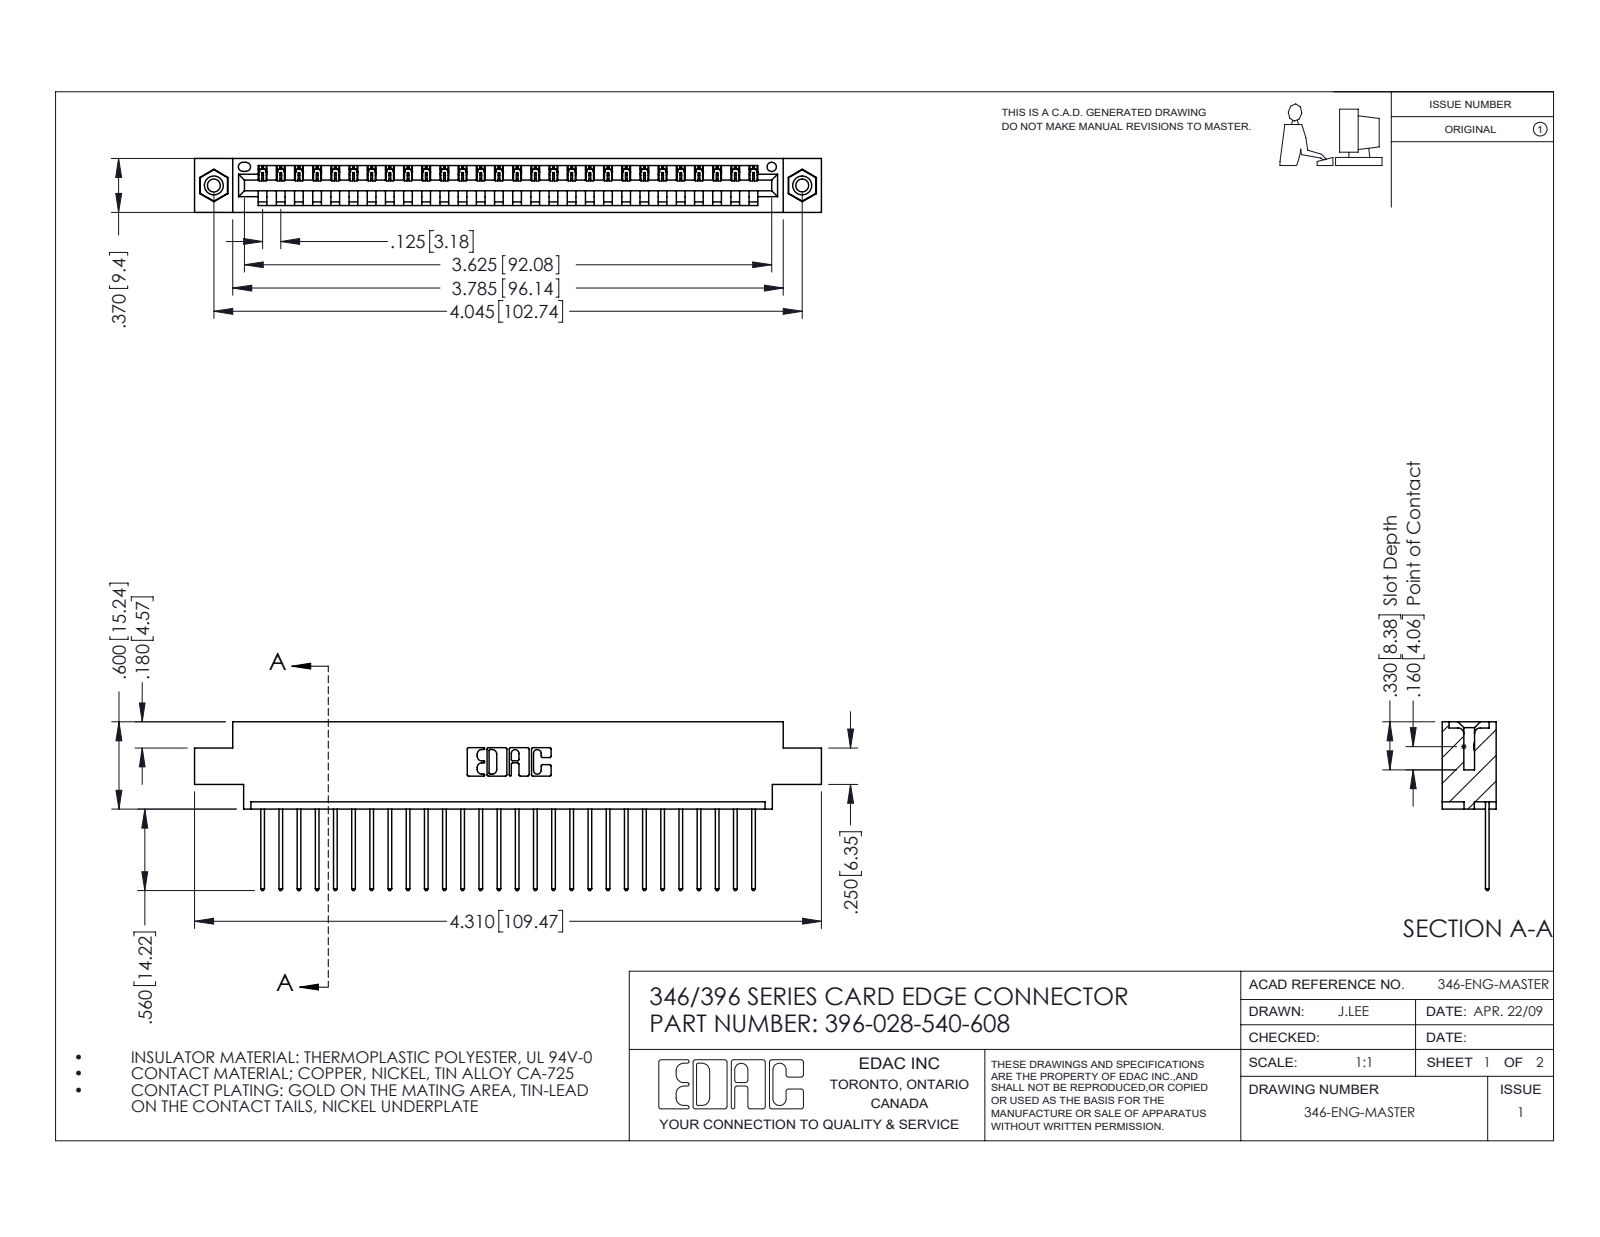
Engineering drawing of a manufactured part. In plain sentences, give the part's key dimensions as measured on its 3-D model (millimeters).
The part is named "345-250-001_345-250-003-102; 346 Part_0.170 Offset - 0.156 Dia-TI; 345-292-001_345-293-140; 396-028-540-608". Its 3-D file was written by "SolidWorks 2016 (CONFIG_CONTROL_DESIGN)". It is 31 solids with 1810 faces: 1232 planar, 562 cylindrical and 16 other. Overall it measures 109.5 by 29.5 by 9.4 millimeters. Its volume is 10 300 cubic millimeters and its surface area 13 130 square millimeters. Round holes: 2 of diameter 2.3, 2 of diameter 3.2, 2 of diameter 4, 1 of diameter 1.6. Round bosses or shafts: 2 of diameter 3.9. Partial cylindrical surfaces (rounded edges, fillets, slot ends): 56 of radius 0.2, 56 of radius 0.3, 22 of radius 0.3, 6 of radius 0.2, 6 of radius 0.8, 3 of radius 0.7, 2 of radius 0.8, 2 of radius 1. The main face-to-face distances are 1.2, 8.2, 9.4, 6.4, 1.8, 7.6, 0.6, 5.6, 3.8, 2.5. The hole center spacings are 6.2, 97.5, 102.7.
